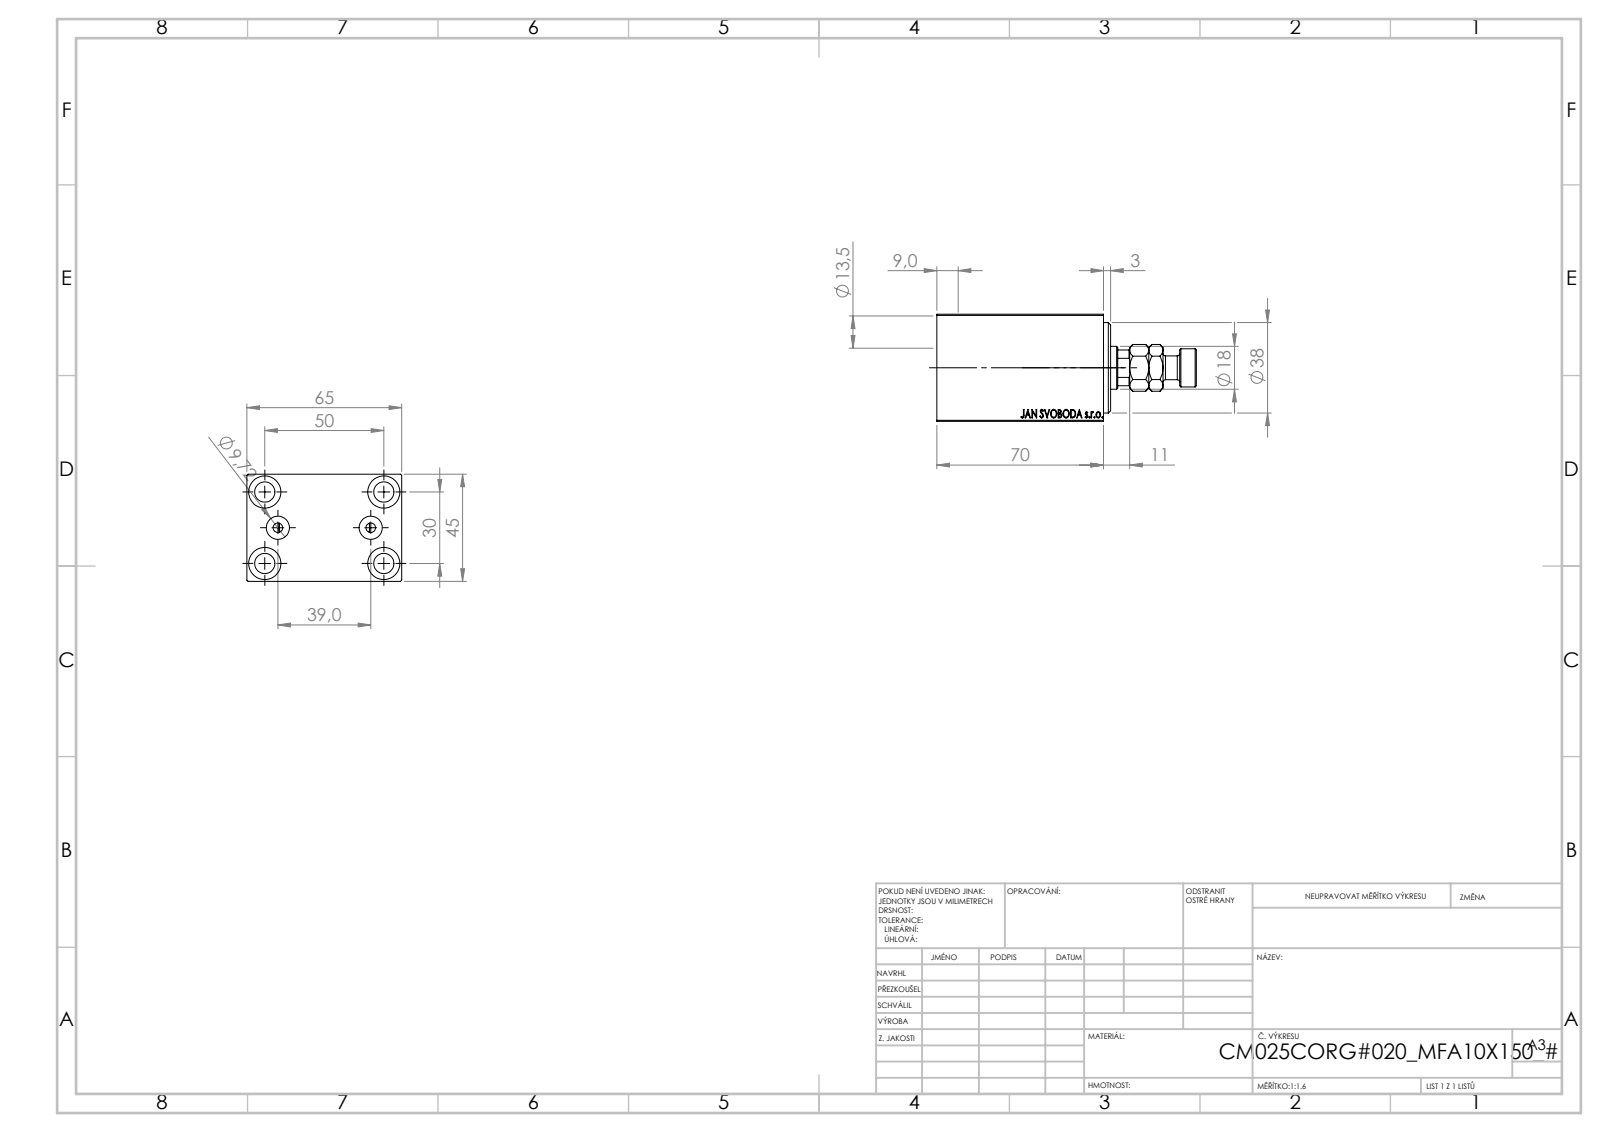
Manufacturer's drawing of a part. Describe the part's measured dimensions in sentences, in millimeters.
The part is named "V450CM_C_Body; MFA; V450CM_C_VCP; V450CM_VC_B". Its 3-D file was written by "SolidWorks 2019 (CONFIG_CONTROL_DESIGN)". It is 4 solids with 910 faces: 424 planar, 60 cylindrical and 426 other. Overall it measures 109 by 65 by 45 millimeters. Its volume is 184 417 cubic millimeters and its surface area 48 984 square millimeters. Round holes: 5 of diameter 8.5, 4 of diameter 13.5, 2 of diameter 4, 2 of diameter 9.72, 1 of diameter 18, 1 of diameter 21.5, 1 of diameter 25, 1 of diameter 27, 1 of diameter 38. Round bosses or shafts: 1 of diameter 16, 1 of diameter 10. Partial cylindrical surfaces (rounded edges, fillets, slot ends): 1 of radius 8.5. The main face-to-face distances are 45, 65, 6, 59, 64, 70, 5, 3, 8, 11. The hole center spacings are 15.98, 29.15, 46.96, 19.5, 30, 50, 58.31, 39.
